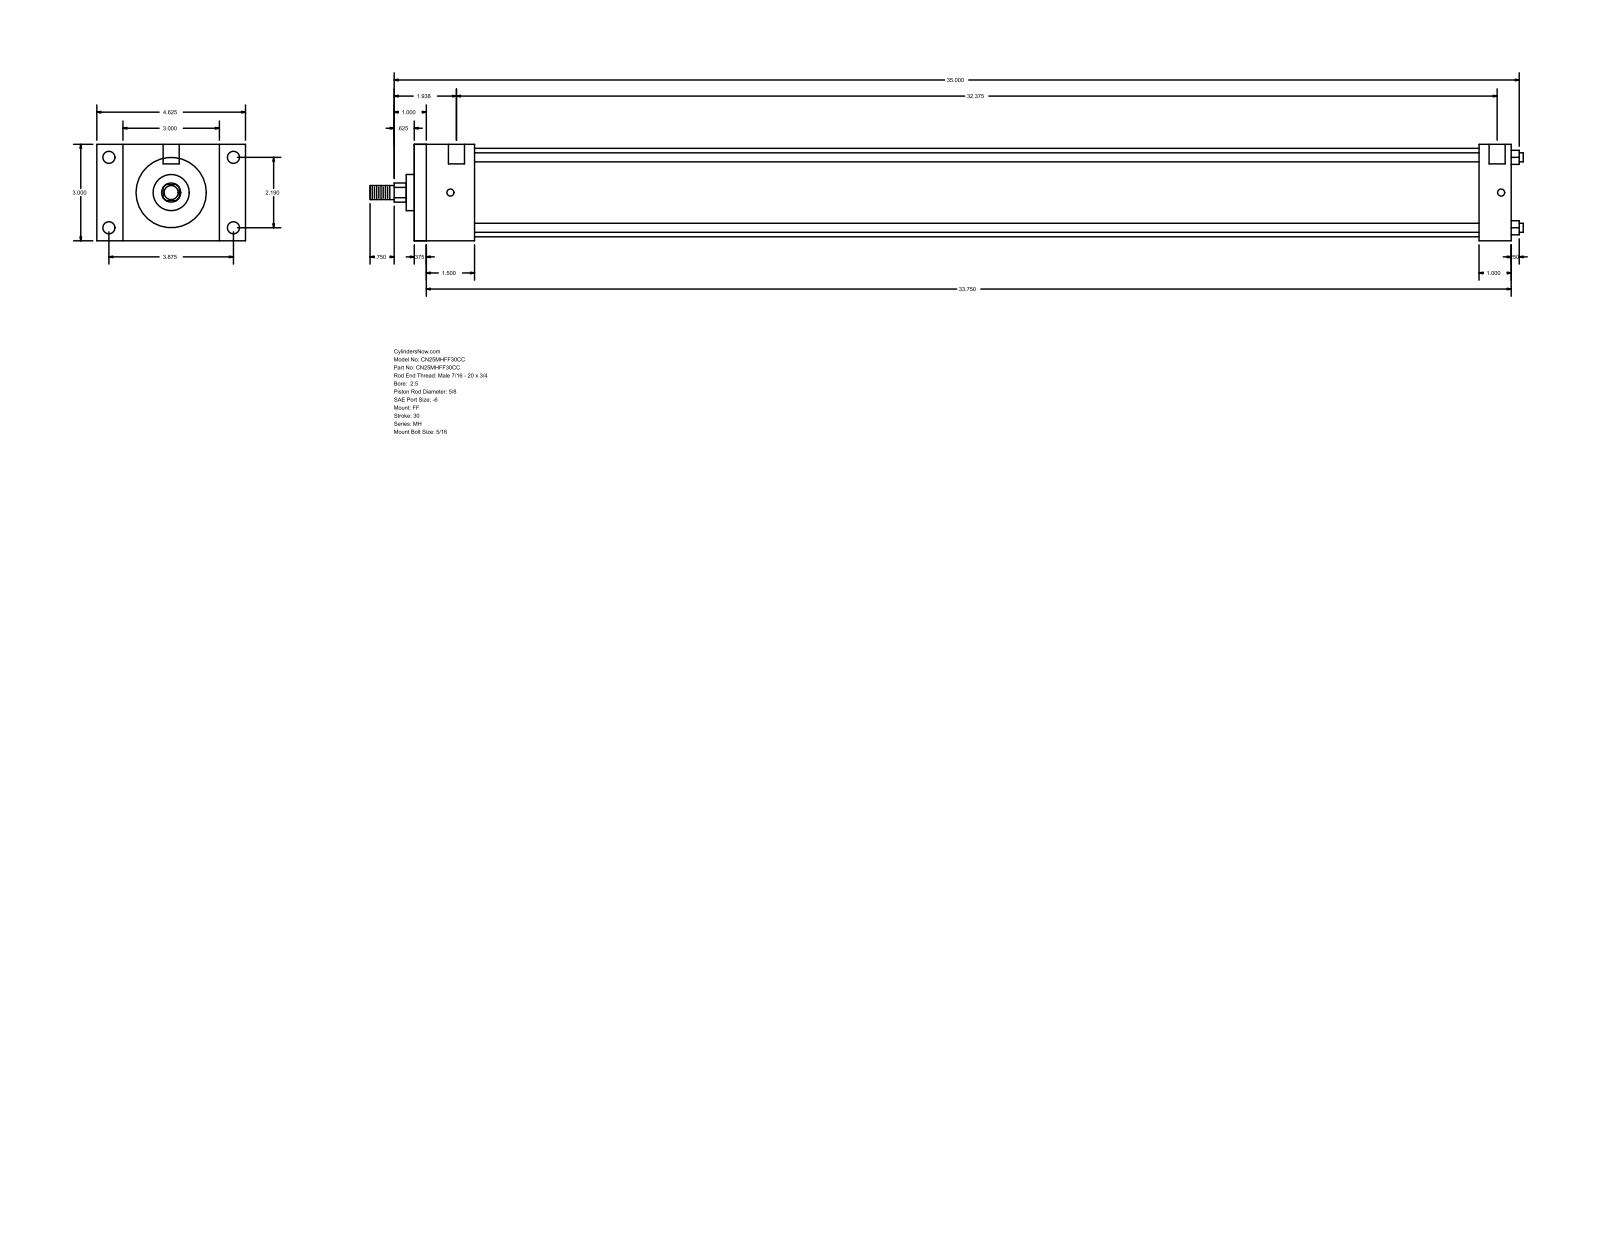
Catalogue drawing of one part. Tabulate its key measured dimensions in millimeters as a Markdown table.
| quantity | value |
| --- | --- |
| part name | MH_FF__0250_0.625 |
| STEP written by | GSSL Pune (CONFIG_CONTROL_DESIGN) |
| units | millimeters |
| bodies | 0 solids, 92 faces (64 planar, 28 cylindrical, 0 other) |
| overall size | 911.23 × 117.47 × 76.2 |
| round holes (diameter × count) | 5.56 × 4, 9.53 × 4, 12.7 × 2 |
| round bosses / shafts (diameter × count) | 7.14 × 4, 69.85 × 1, 28.57 × 1, 15.88 × 1, 11.11 × 1 |
| partial cylindrical surfaces (radius × count) | 7.54 × 1 |
| main face-to-face distances | 76.2, 866.77, 9.52, 857.25, 25.4, 47.62, 841.37, 38.1, 831.85, 793.75 |
| hole center spacings | 55.62, 98.42, 113.05, 830.26, 3.17, 4.76, 822.33, 825.5 |
